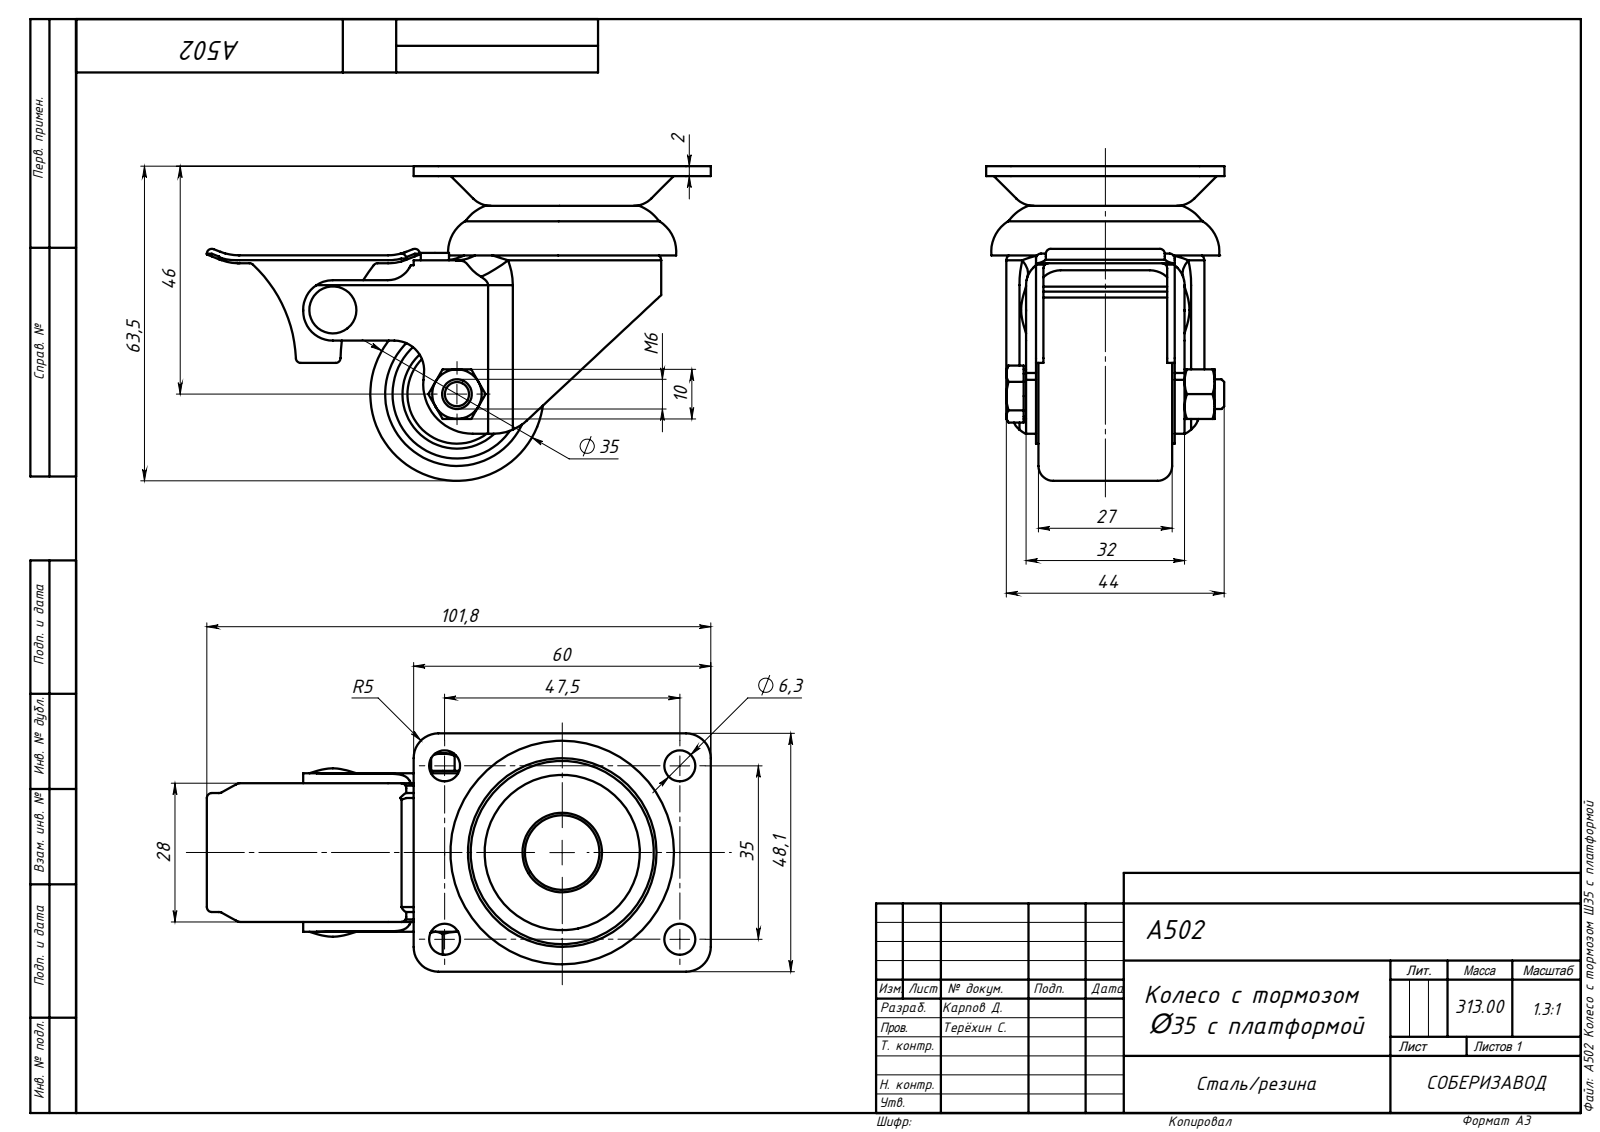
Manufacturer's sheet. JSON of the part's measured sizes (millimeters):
{"part_name": "Площадка A502_00; Дно A502_00; Крышка A502_00; Колесо A502_00 (+7 more)", "step_written_by": "SolidWorks 2020 (AUTOMOTIVE_DESIGN)", "units": "millimeters", "bodies": {"solids": 12, "faces": 352, "planar": 113, "cylindrical": 128, "other": 111}, "overall_size": [101.76, 63.5, 48.1], "volume_mm3": 54122, "surface_area_mm2": 38381, "round_holes": [[6.25, 4], [5, 2], [10, 2], [6, 1], [8, 1], [12, 1], [22, 1]], "round_bosses_or_shafts": [[5.7, 2], [35, 1], [20, 1], [16.05, 1]], "partial_cylinders_radius": [[1, 27], [5, 9], [10, 8], [6, 3], [18, 1], [20, 1], [27.38, 1], [31.26, 1]], "face_to_face_distances": [2, 6, 4, 28, 13, 19, 30, 8, 1.5, 11], "hole_center_spacings": [29.5, 35, 47.5, 59, 30.28]}
